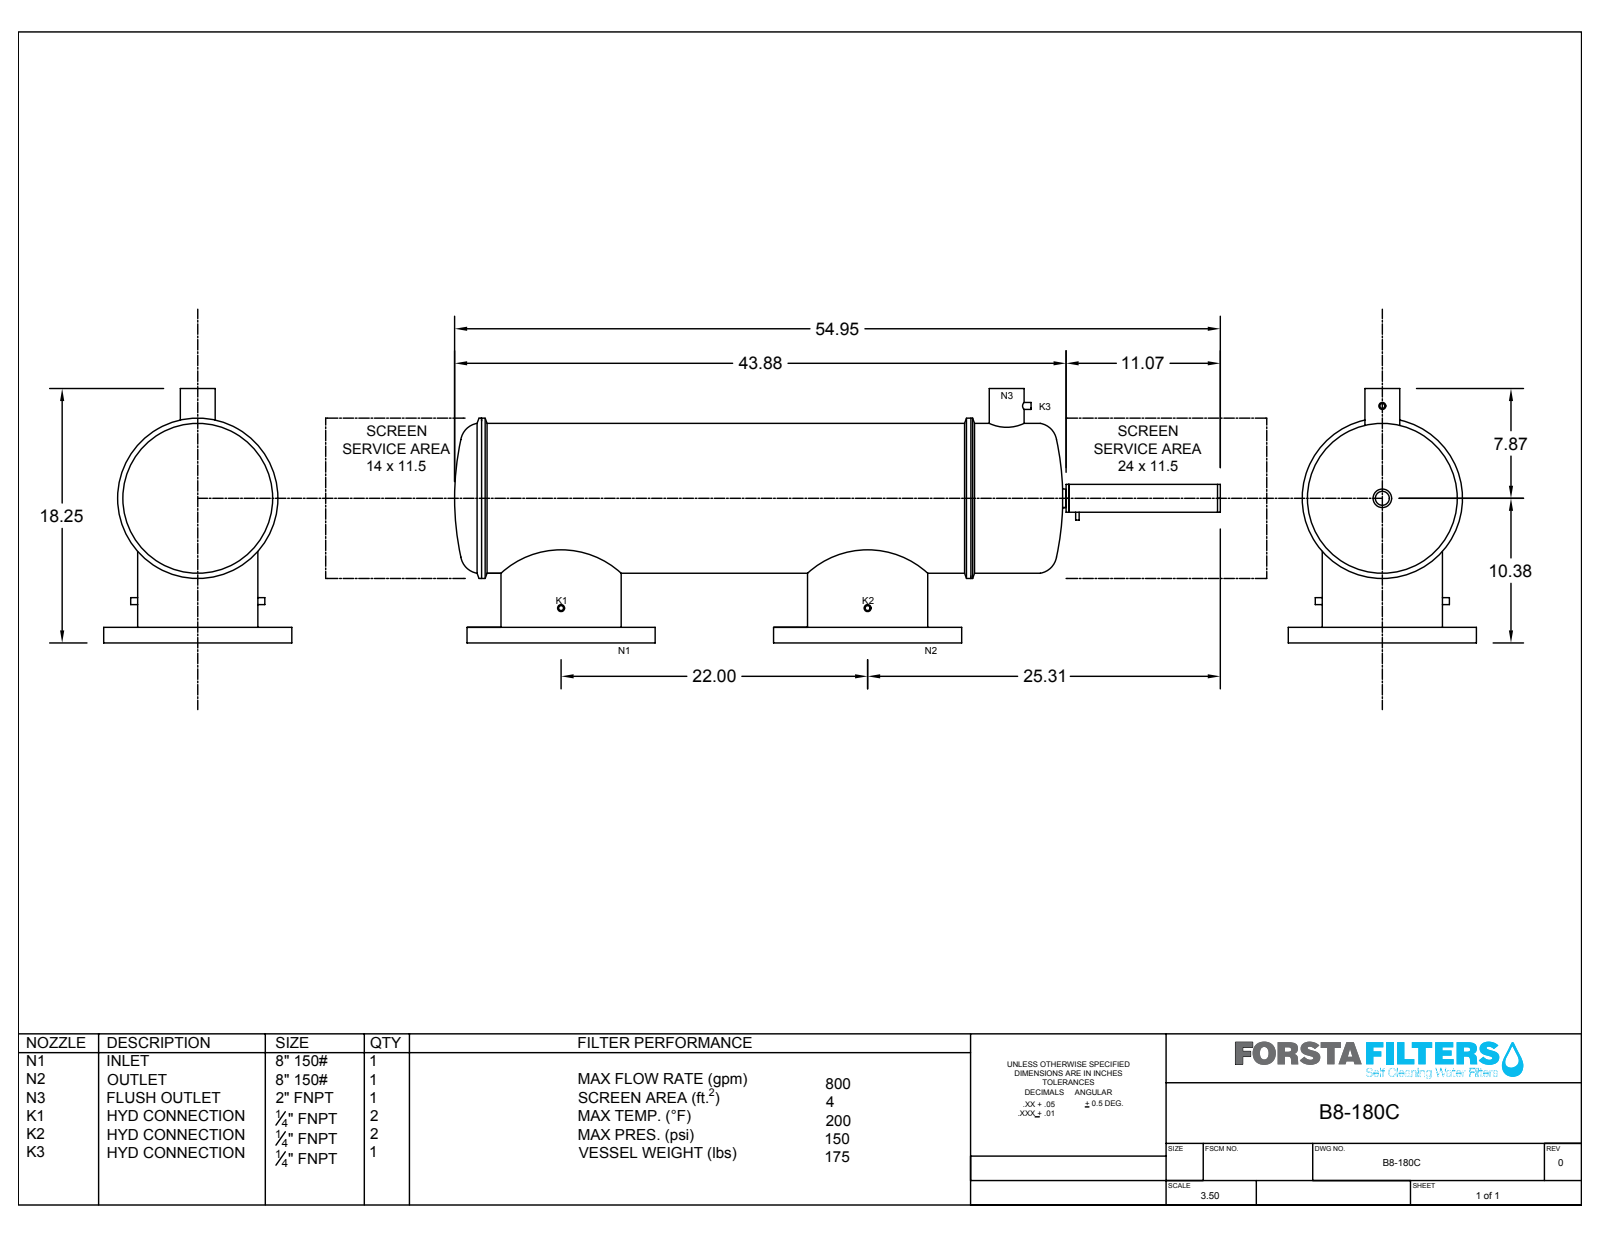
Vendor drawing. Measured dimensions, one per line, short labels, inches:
name: B8-180C
written by: SolidWorks 2017 (CONFIG_CONTROL_DESIGN)
unit: in
bodies: 6 solids, 176 faces (40 planar, 100 cylindrical, 36 other)
size: 61.622 × 18.25 × 13.5
volume: 608.5 in³; area: 4 478 in²
holes: 16× ⌀0.88, 3× ⌀0.25, 2× ⌀1, 2× ⌀8, 1× ⌀0.093, 1× ⌀0.936, 1× ⌀2, 1× ⌀10.356
bosses: 3× ⌀0.644, 2× ⌀13.5, 2× ⌀8.394, 1× ⌀11.5, 1× ⌀10.75, 1× ⌀2.394, 1× ⌀2, 1× ⌀1.33
rounds: 2× R1
face distances: 1.12, 0.25, 0.2, 14.042, 59.485, 45.643, 13.842, 45.443, 59.685, 14.242
hole spacings: 4.496, 5.875, 10.856, 24.4, 8.308, 8.309, 4.497, 5.875
